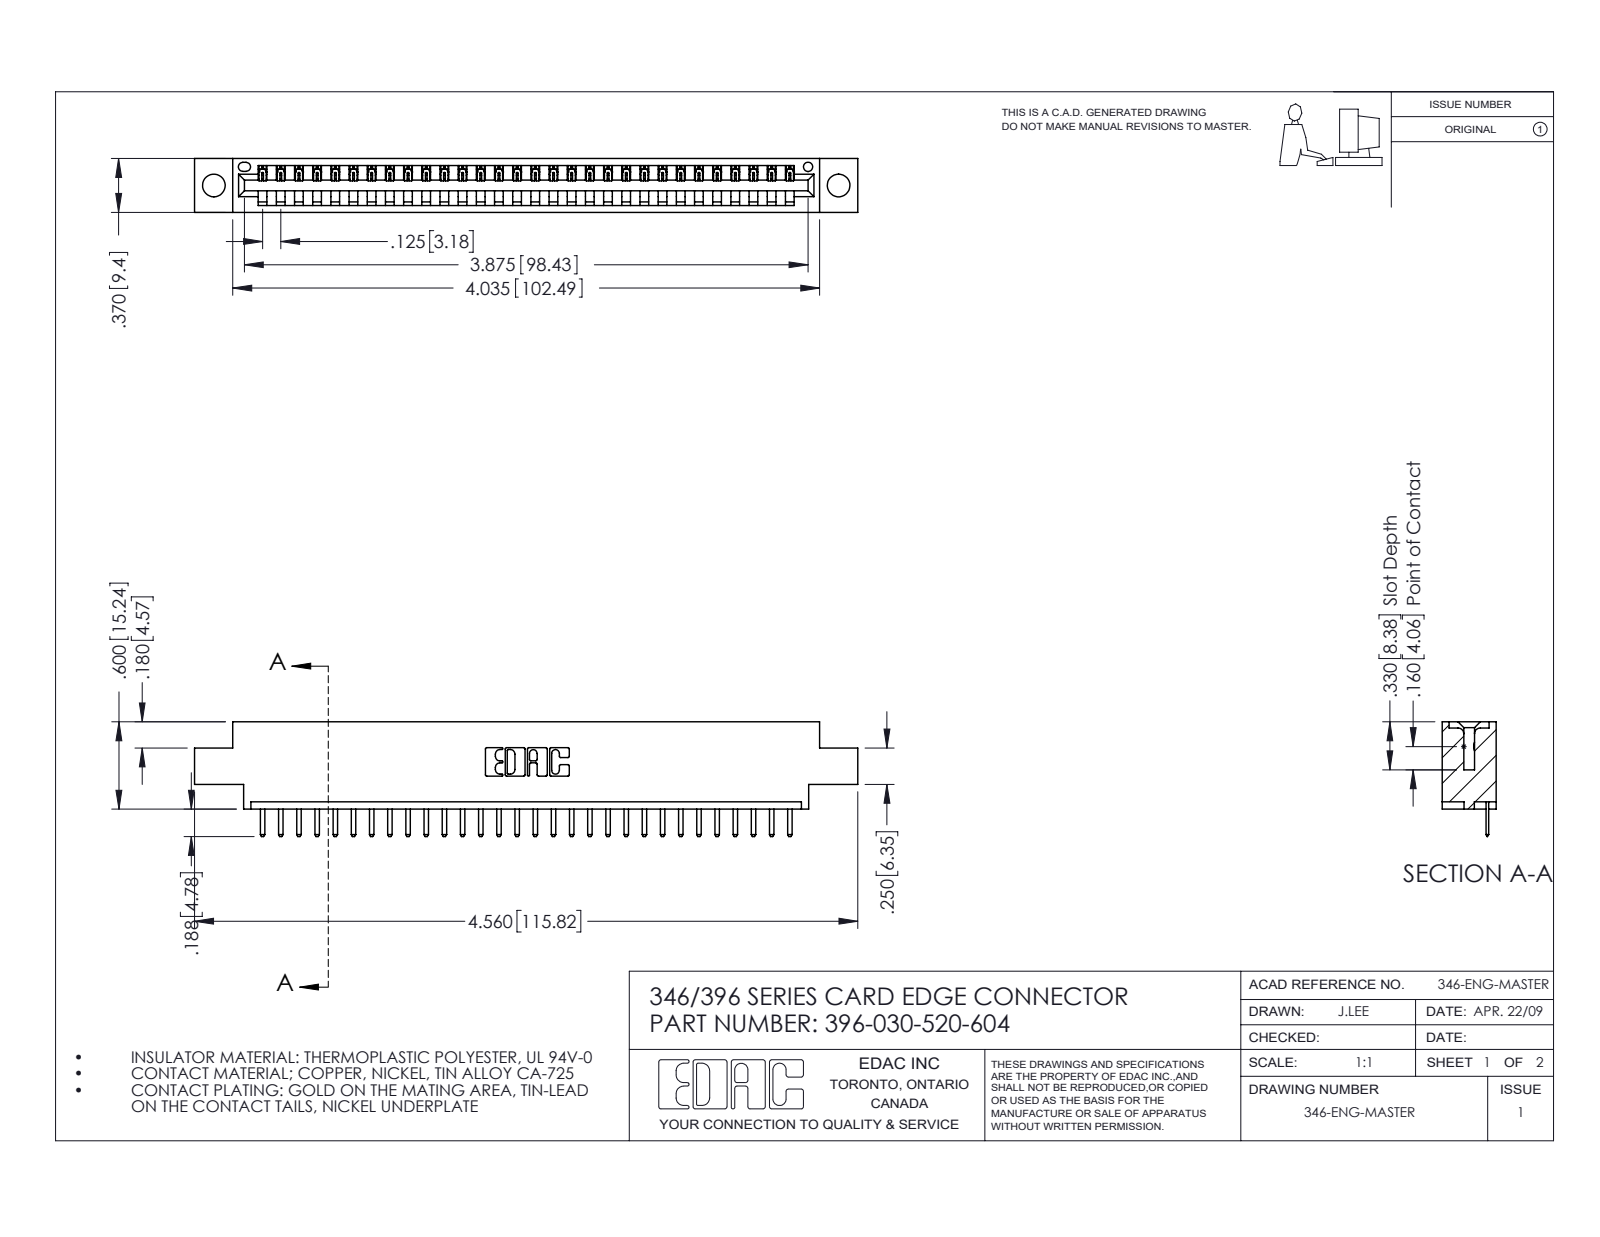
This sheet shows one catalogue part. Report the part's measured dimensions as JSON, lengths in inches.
{"part_name": "346 Part_0.170 Offset - 0.156 Dia-TH; 345-292-001_345-293-120; 396-030-520-604", "step_written_by": "SolidWorks 2016 (CONFIG_CONTROL_DESIGN)", "units": "inches", "bodies": {"solids": 31, "faces": 1986, "planar": 1340, "cylindrical": 646, "other": 0}, "overall_size": [4.56, 0.788, 0.37], "volume_in3": 0.651, "surface_area_in2": 19.98, "round_holes": [[0.156, 2], [0.064, 1]], "partial_cylinders_radius": [[0.01, 62], [0.006, 60], [0.01, 22], [0.007, 6], [0.031, 6], [0.026, 3], [0.031, 2], [0.04, 2]], "face_to_face_distances": [0.048, 0.322, 0.37, 0.25, 0.148, 0.222, 0.1, 0.174, 0.072, 0.298], "hole_center_spacings": [0.246, 4.087, 4.295]}
